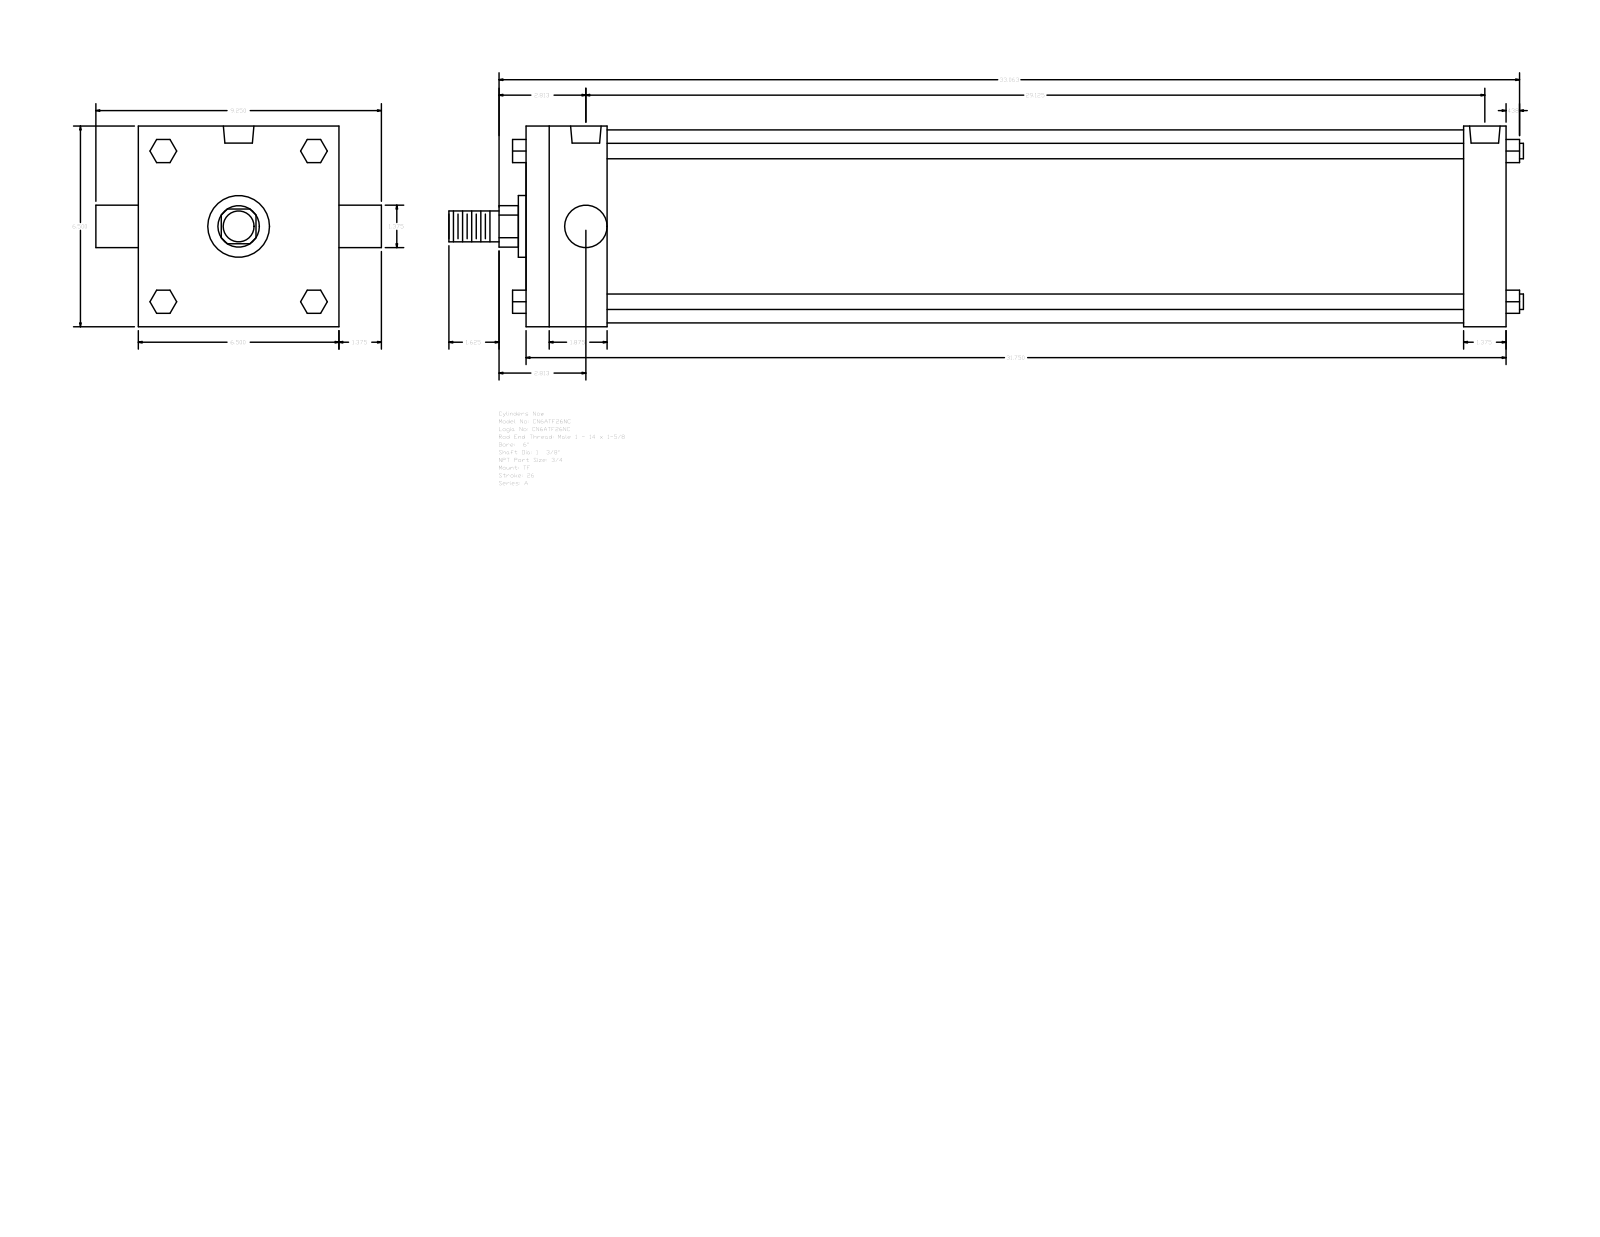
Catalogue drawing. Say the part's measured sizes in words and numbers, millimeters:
The part is named "A_TF__0600_1.375". Its 3-D file was written by "GSSL Pune (CONFIG_CONTROL_DESIGN)". It is 0 solids with 120 faces: 92 planar, 28 cylindrical and 0 other. Overall it measures 884.24 by 234.95 by 165.1 millimeters. Round holes: 3 of diameter 15.08, 2 of diameter 25.12. Round bosses or shafts: 4 of diameter 12.7, 2 of diameter 34.92, 1 of diameter 158.75, 1 of diameter 50.8, 1 of diameter 25.4. Partial cylindrical surfaces (rounded edges, fillets, slot ends): 1 of radius 17.06. The main face-to-face distances are 165.1, 806.44, 34.92, 66.67, 739.77, 771.52, 704.85, 19.05, 61.97, 107.34. The hole center spacings are 5.56, 734.21, 728.65, 739.77.
